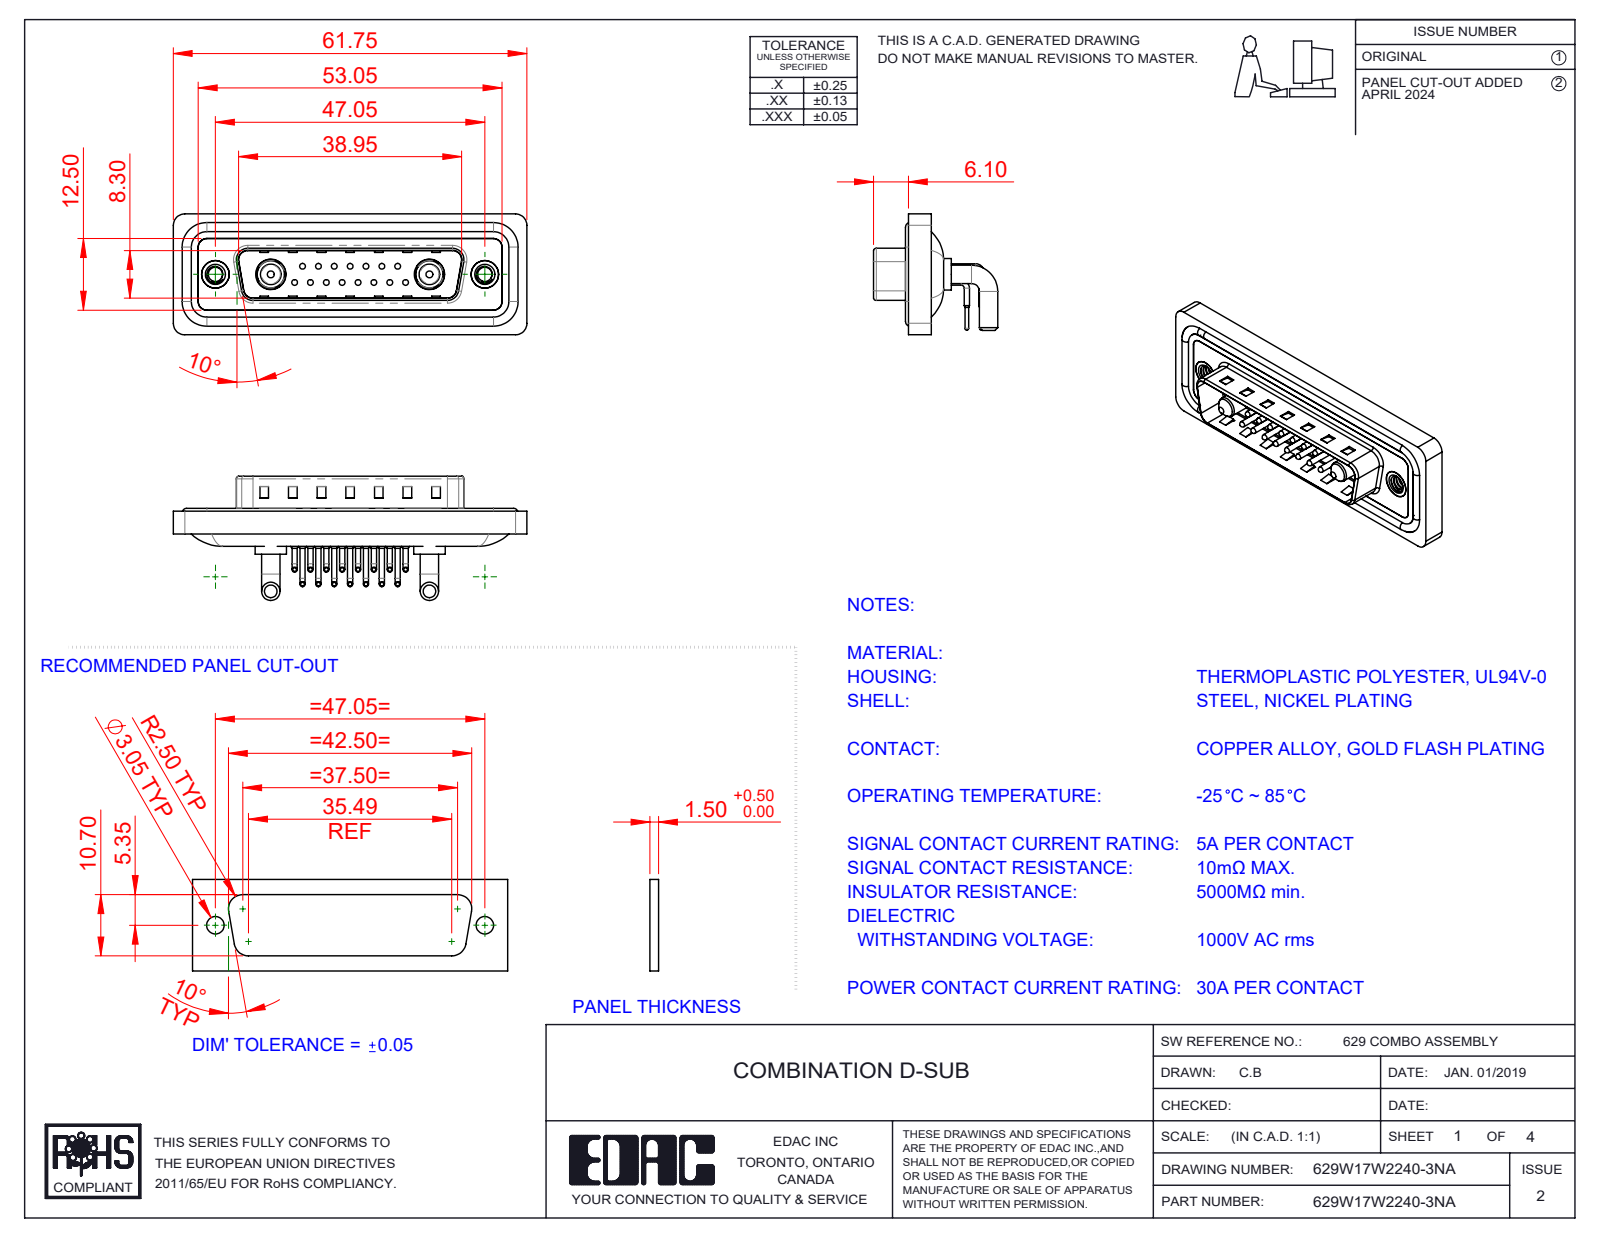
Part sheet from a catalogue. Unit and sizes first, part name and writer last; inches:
Units: inches
Overall size (bounding box): 2.431 × 0.854 × 0.831
Round holes (diameter × count): ⌀0.03 ×15, ⌀0.063 ×15, ⌀0.079 ×15, ⌀0.098 ×2, ⌀0.157 ×2, ⌀0.189 ×2, ⌀0.191 ×2, ⌀0.197 ×2, ⌀0.209 ×2
Round bosses / shafts (diameter × count): ⌀0.035 ×30, ⌀0.059 ×15, ⌀0.039 ×15, ⌀0.026 ×15, ⌀0.126 ×4, ⌀0.063 ×4, ⌀0.217 ×2, ⌀0.205 ×2
Partial cylindrical surfaces — rounded edges, fillets, slot ends (radius × count): R0.059 ×18, R0.079 ×18, R0.04 ×15, R0.02 ×8, R0.063 ×8, R0.01 ×4, R0.024 ×4, R0.026 ×4
Main face-to-face distances: 0.016, 0.114, 0.031, 0.161, 0.043, 0.083, 0.063, 0.177, 0.059, 0.098
Hole centre spacings: 0.124, 0.109, 0.218, 0.327, 0.198, 0.295, 0.436, 0.198
Volume: 0.462 in³ · Surface area: 19.6 in²
Bodies: 26 solids, 2213 faces (1189 planar, 768 cylindrical, 256 other)
Part name (STEP PRODUCT): 629Combo Waterproof Housing_25 Contacts; 629Combo Threaded Rivet_A; 629W17W2140-3NA; 629Combo Contact Row 2 (+5 more)
STEP written by: SolidWorks 2023 (CONFIG_CONTROL_DESIGN)
